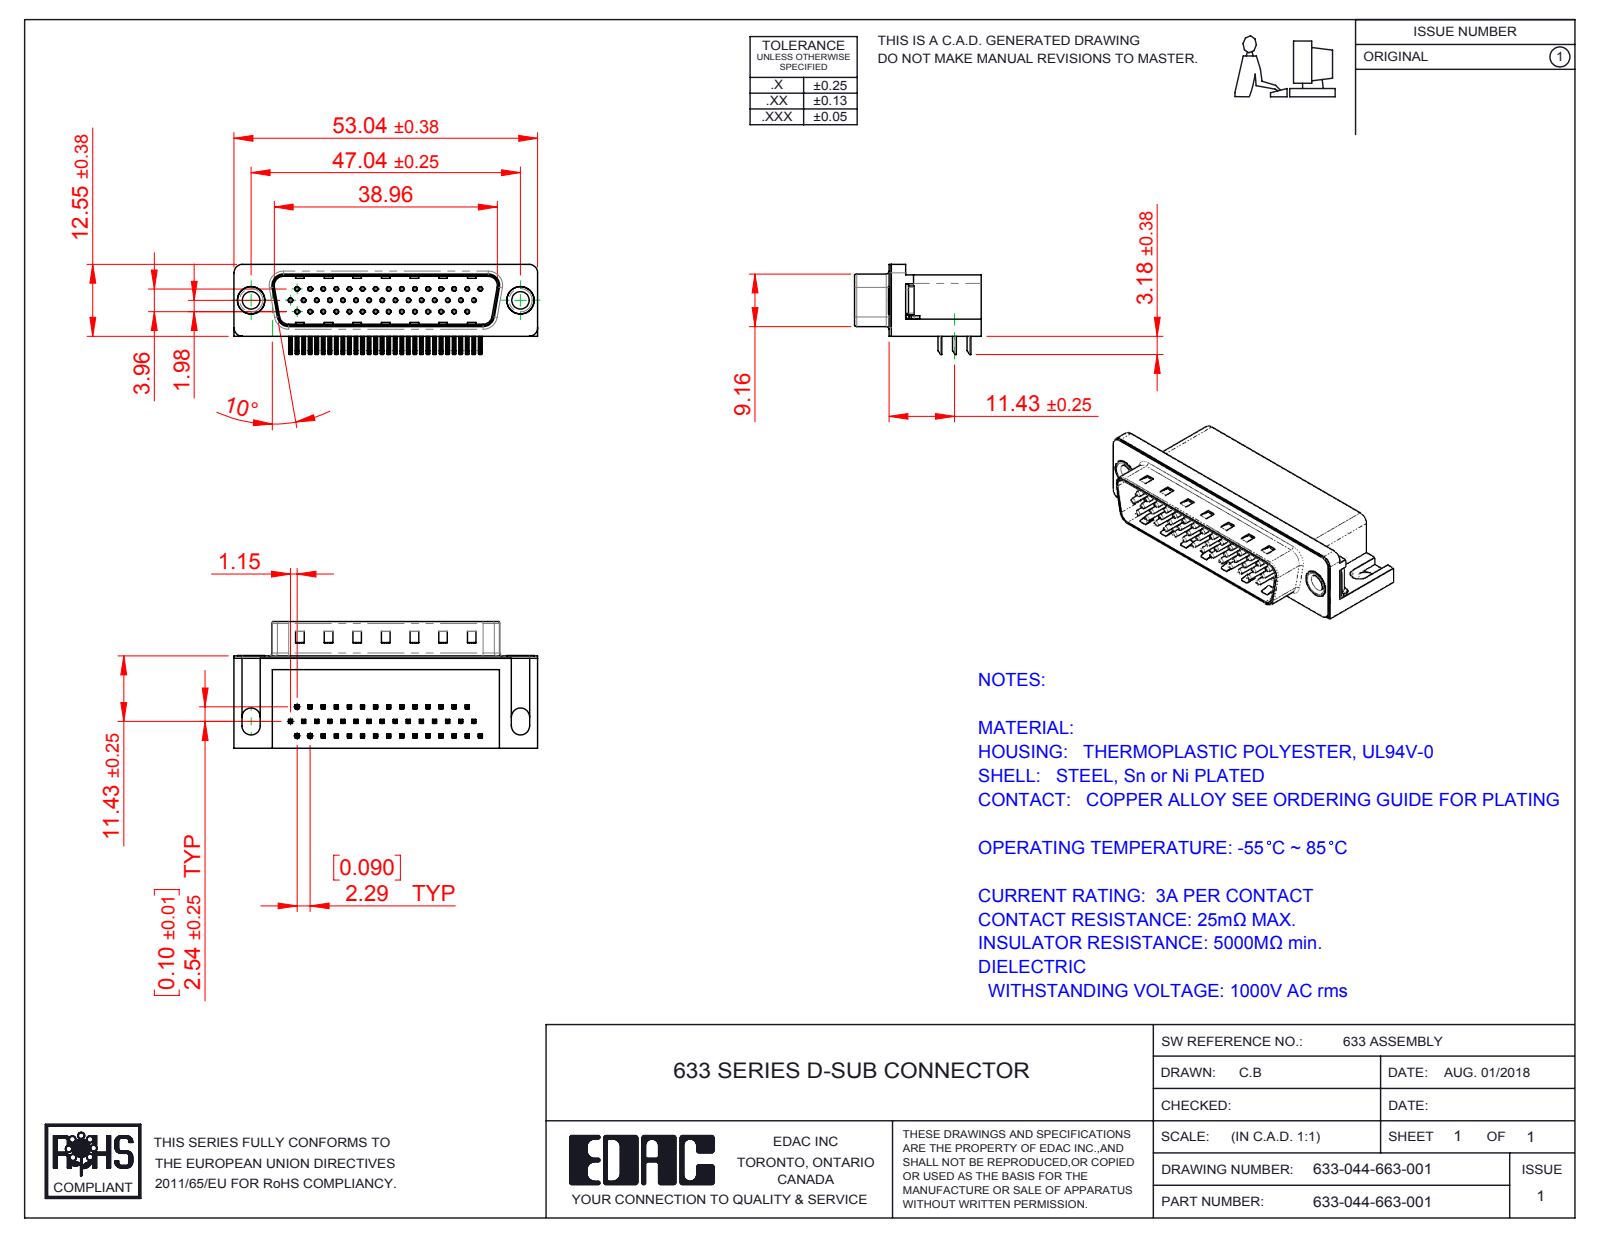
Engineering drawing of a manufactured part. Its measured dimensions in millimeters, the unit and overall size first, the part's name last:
Units: millimetres
Overall size (bounding box): 53.04 × 22.1 × 15.73
Round holes (diameter × count): ⌀0.35 ×44, ⌀0.8 ×44, ⌀3.05 ×2, ⌀4 ×2, ⌀4.8 ×2, ⌀5 ×2
Round bosses / shafts (diameter × count): ⌀0.75 ×44, ⌀4.9 ×2, ⌀4.75 ×2, ⌀3.85 ×2
Partial cylindrical surfaces — rounded edges, fillets, slot ends (radius × count): R0.25 ×184, R0.12 ×88, R1 ×16, R0.5 ×9, R1.6 ×8, R1.5 ×7, R0.9 ×4, R2 ×4
Main face-to-face distances: 0.4, 10.35, 15.7, 8.76, 2.9, 2.5, 2.1, 16.1, 10.7, 2.54
Hole centre spacings: 2.29, 4.57, 4.58, 2.28, 6.87, 9.16, 11.45, 2.27
Volume: 8 056 mm³ · Surface area: 9 976 mm²
Bodies: 50 solids, 3646 faces (2317 planar, 1038 cylindrical, 291 other)
Part name (STEP PRODUCT): 633 Shell_44 Contact; 633 Thru Hole Rivet; 633 Non Board Mount; 633 Contact Middle (+4 more)
STEP written by: SolidWorks 2016 (CONFIG_CONTROL_DESIGN)
